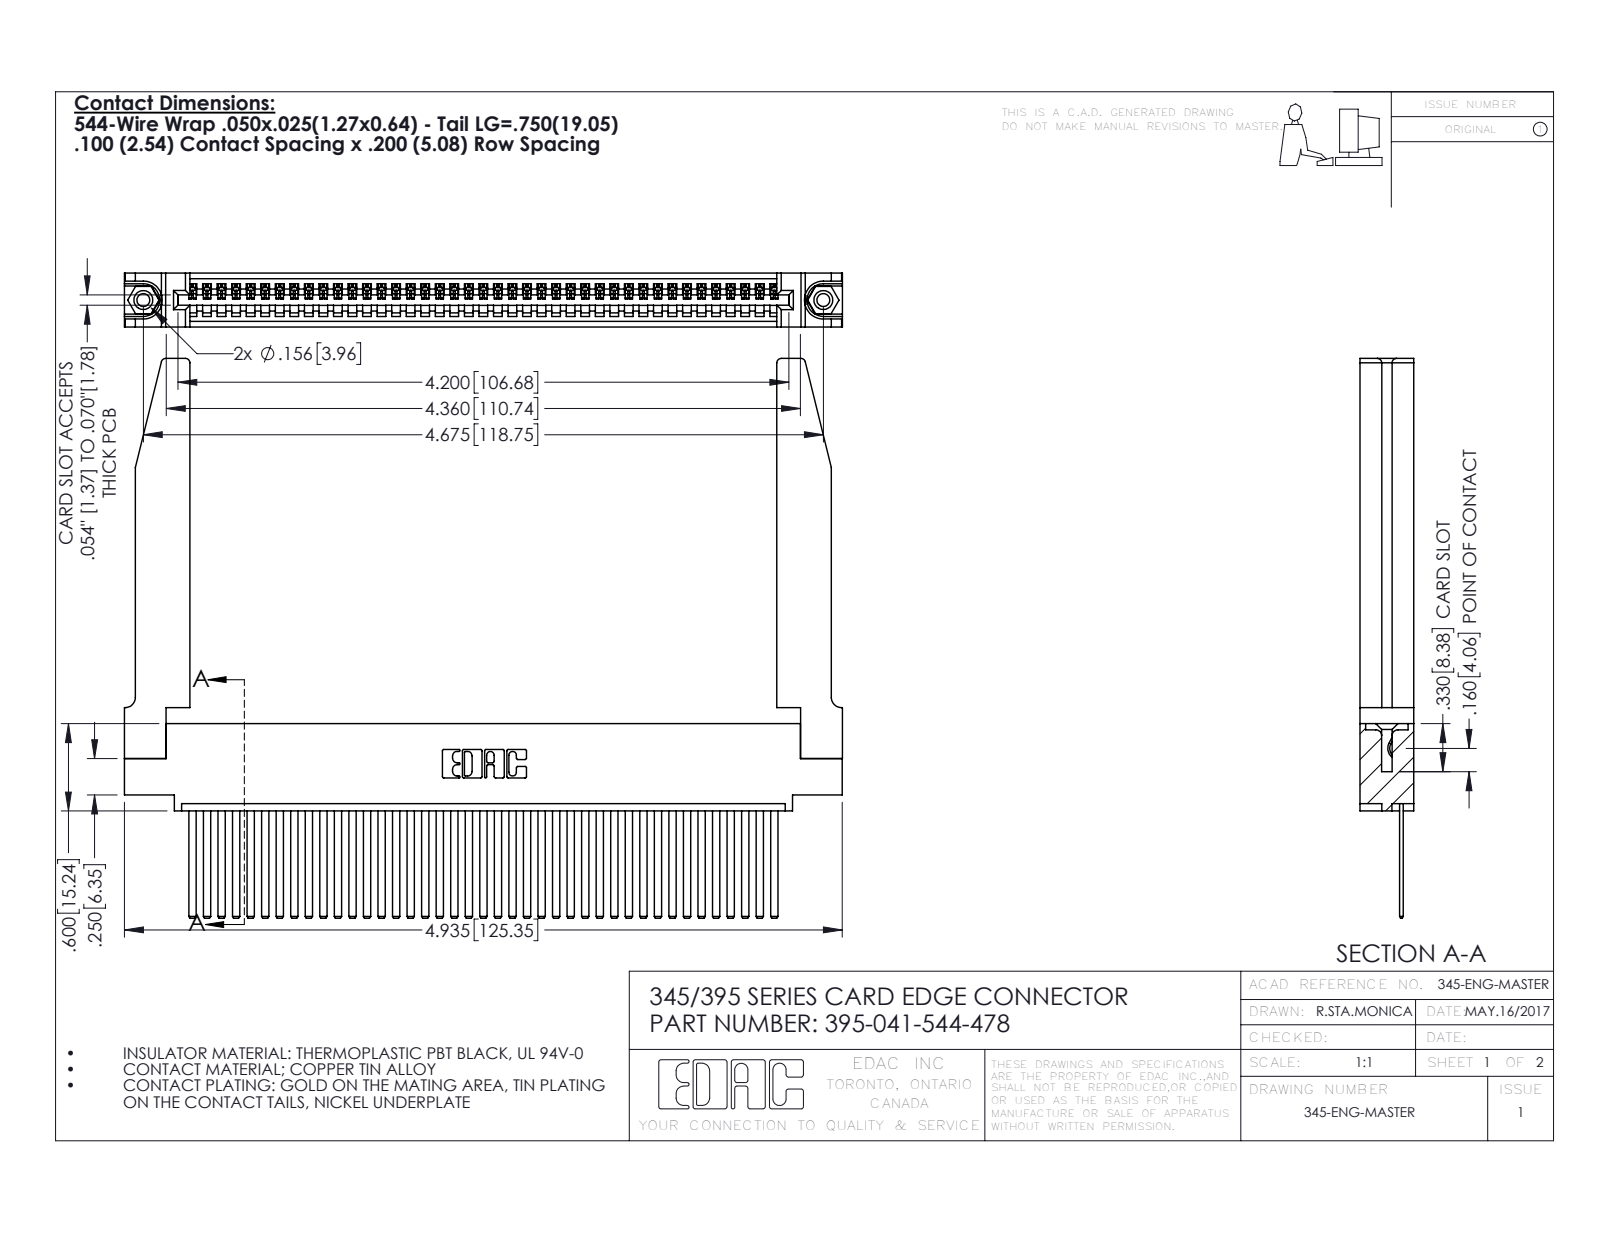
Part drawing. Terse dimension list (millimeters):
name: 345-220-078_345-220-078; 345-250-001_345-250-001-102; 345-292-001_345-293-144; 395-041-544-478 (+1 more)
written by: SolidWorks 2016 (CONFIG_CONTROL_DESIGN)
unit: mm
bodies: 46 solids, 2496 faces (1702 planar, 742 cylindrical, 52 other)
size: 125.4 × 97.7 × 9.4
volume: 20 070 mm³; area: 24 680 mm²
holes: 2× ⌀2.3, 2× ⌀3.2, 2× ⌀4, 1× ⌀1.6
bosses: 2× ⌀3.9
rounds: 82× R0.2, 22× R0.3, 8× R0.8, 6× R0.2, 6× R0.8, 3× R0.7, 2× R0.8, 2× R1
face distances: 1.8, 7.6, 9.4, 2.5, 6.9, 0.6, 5.1, 5.7, 3.8, 3.8
hole spacings: 6.9, 112.8, 118.7
